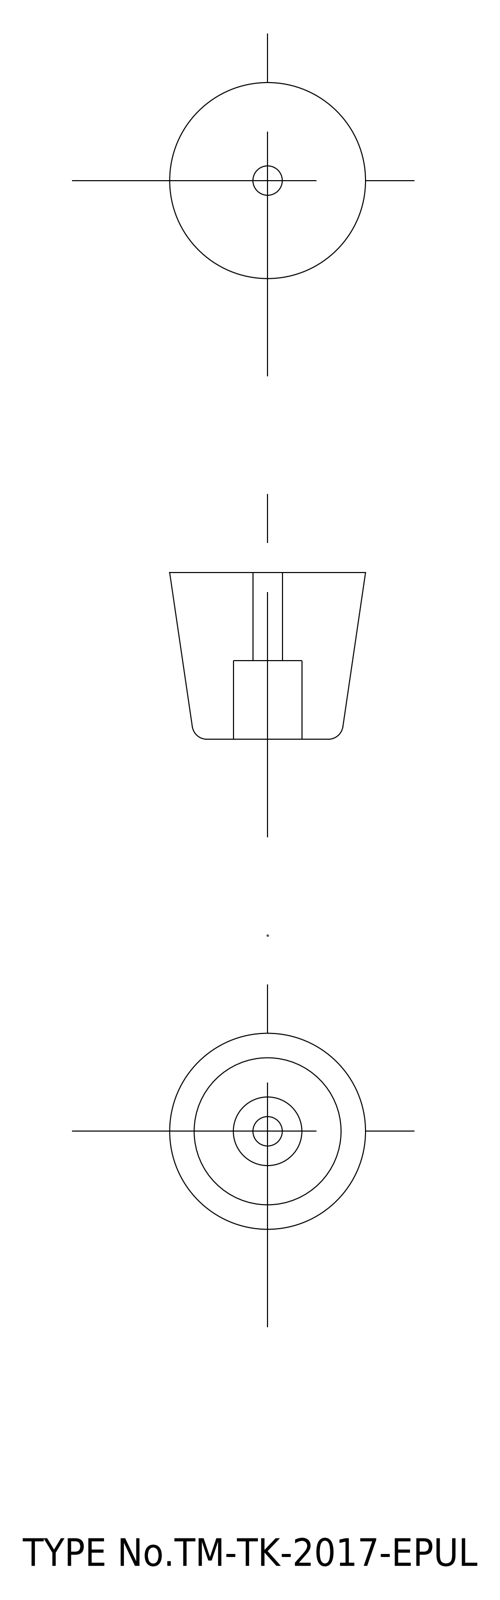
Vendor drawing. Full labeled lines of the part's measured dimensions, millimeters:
Part name (STEP PRODUCT): washer; rubber foot
STEP written by: spGate 15.6.1 (AUTOMOTIVE_DESIGN)
Units: millimetres
Bodies: 2 solids, 23 faces (7 planar, 12 cylindrical, 4 other)
Overall size (bounding box): 20 × 20 × 17
Volume: 3 738 mm³ · Surface area: 1 859 mm²
Round holes (diameter × count): ⌀3 ×1, ⌀3.5 ×1, ⌀7 ×1, ⌀9 ×1
Main face-to-face distances: 8.5, 17, 8, 0.5, 9
